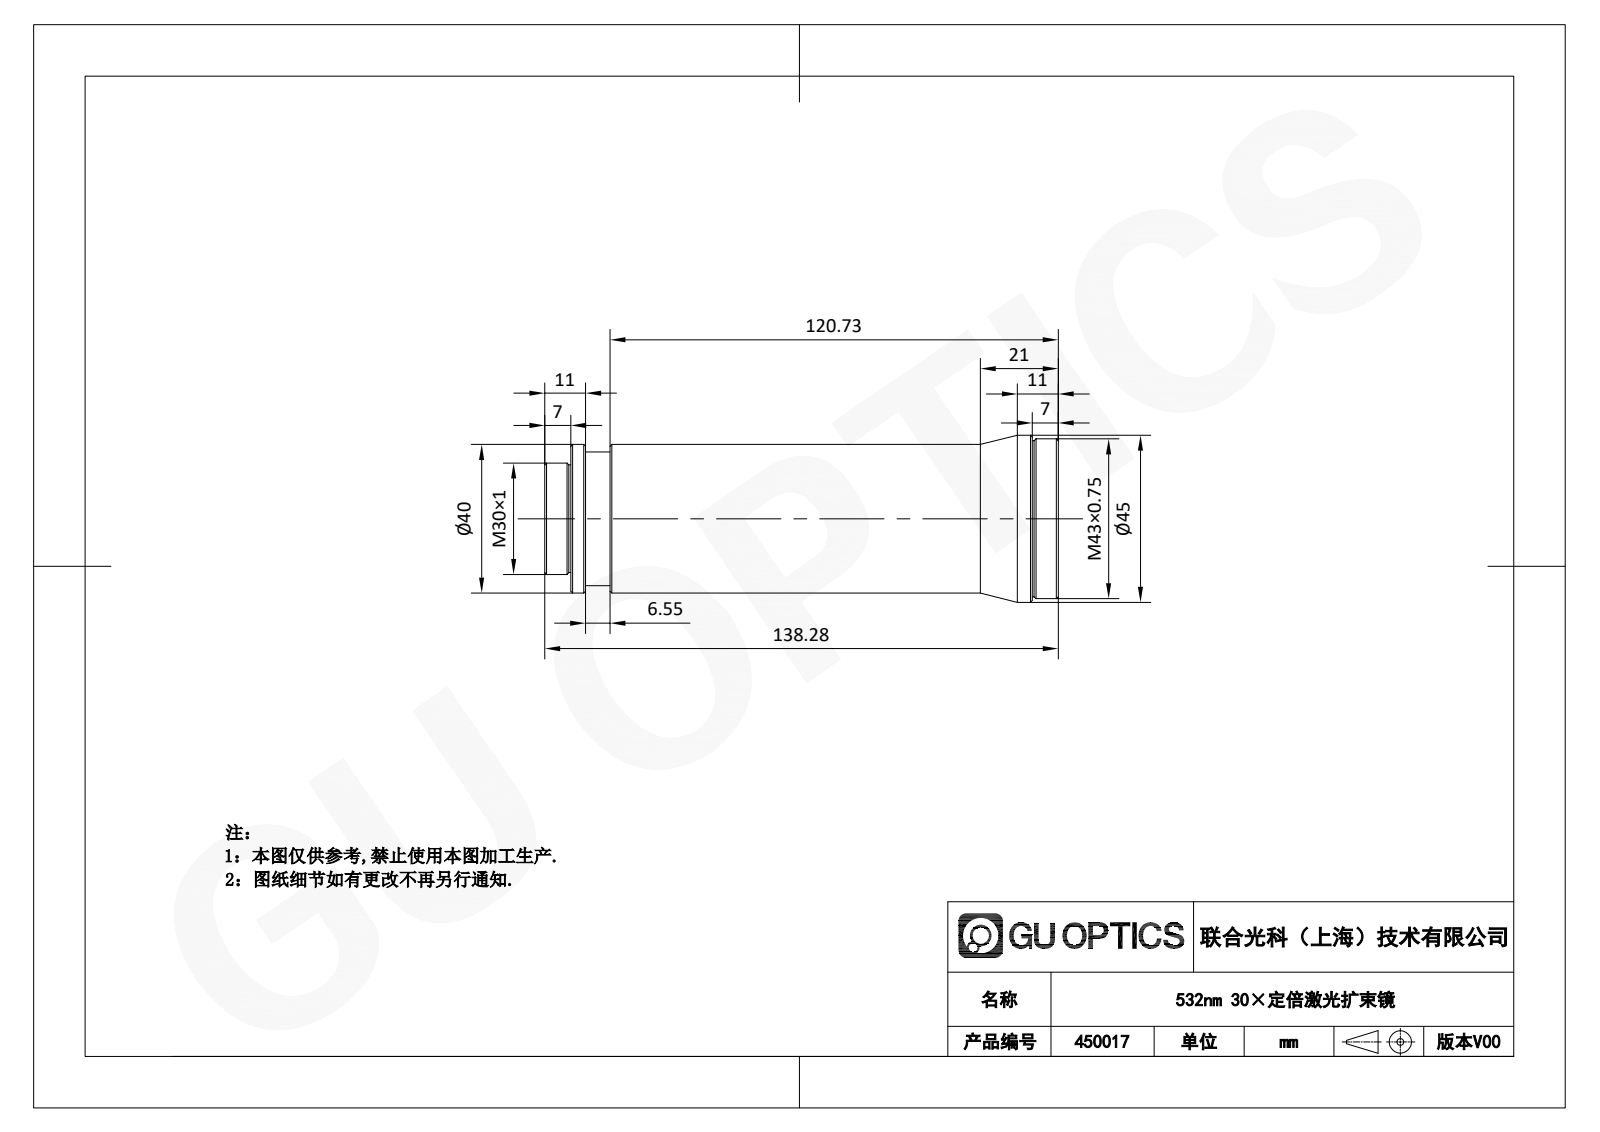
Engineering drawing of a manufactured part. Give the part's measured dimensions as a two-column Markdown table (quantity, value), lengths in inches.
| quantity | value |
| --- | --- |
| part name | 450028 |
| STEP written by | SolidWorks 2020 (CONFIG_CONTROL_DESIGN) |
| units | inches |
| bodies | 1 solid, 46 faces (8 planar, 20 cylindrical, 18 other) |
| overall size | 5.444 × 1.772 × 1.772 |
| volume | 10.44 in³ |
| surface area | 32.25 in² |
| round holes (diameter × count) | 0.236 × 1, 1.181 × 1 |
| round bosses / shafts (diameter × count) | 1.772 × 1, 1.693 × 1, 1.654 × 1, 1.575 × 1, 1.417 × 1, 1.142 × 1 |
| main face-to-face distances | 0.079, 0.276, 5.169, 5.365, 5.444, 5.09, 0.691, 0.415, 4.674, 4.753 |
